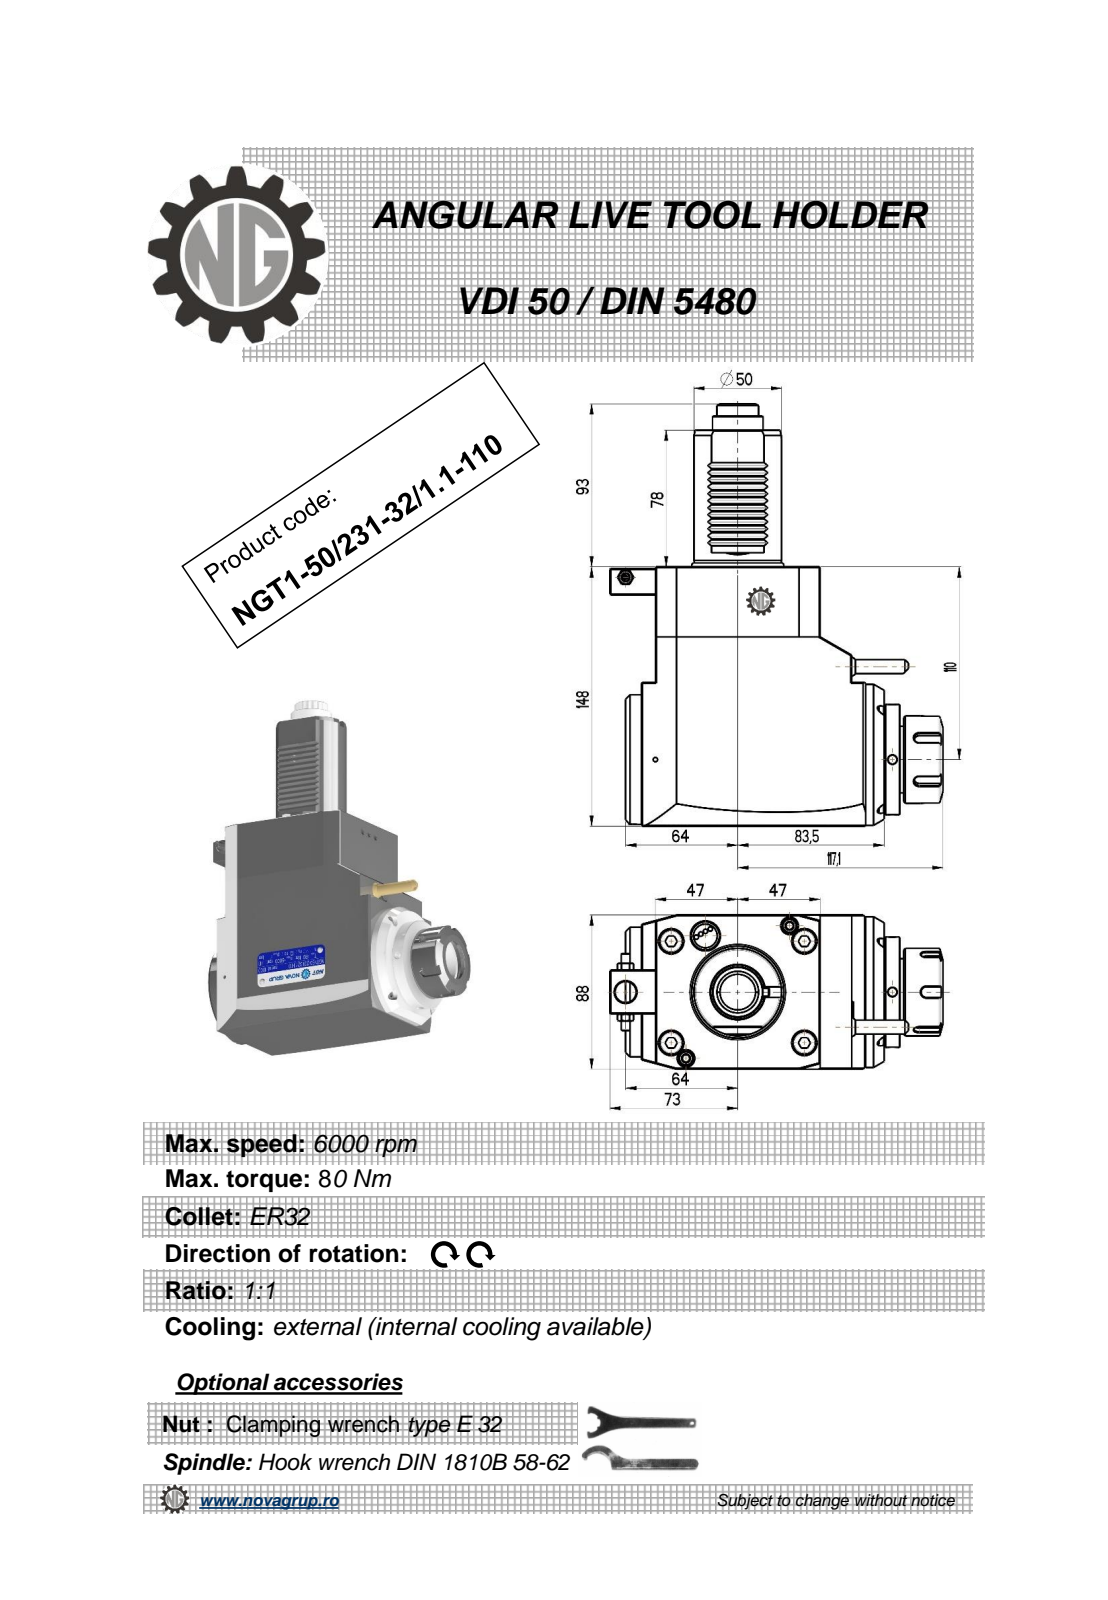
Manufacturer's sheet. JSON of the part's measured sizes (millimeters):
{"part_name": "NGT1_50_231_32_1_1_110", "step_written_by": "PRO/ENGINEER BY PARAMETRIC TECHNOLOGY CORPORATION, 2010280 (CONFIG_CONTROL_DESIGN)", "units": "millimeters", "bodies": {"solids": 1, "faces": 498, "planar": 190, "cylindrical": 157, "other": 151}, "overall_size": [241, 190.1, 88], "volume_mm3": 1811000, "surface_area_mm2": 111922, "round_holes": [[5, 3], [3, 1], [4.2, 1], [9.5, 1], [12, 1], [27, 1]], "round_bosses_or_shafts": [[50, 2], [86, 1], [74, 1], [63, 1], [50.5, 1], [41, 1], [28.8, 1], [10, 1]], "partial_cylinders_radius": [[3.04, 36], [0.26, 12], [0.3, 12], [0.2, 6], [3, 5], [10.56, 1], [11.88, 1], [17.5, 1]], "face_to_face_distances": [88, 148, 147.5, 9, 94, 17, 8, 111, 120, 36.5], "hole_center_spacings": [52.46, 56.65, 101.5, 152.25, 184.38]}
